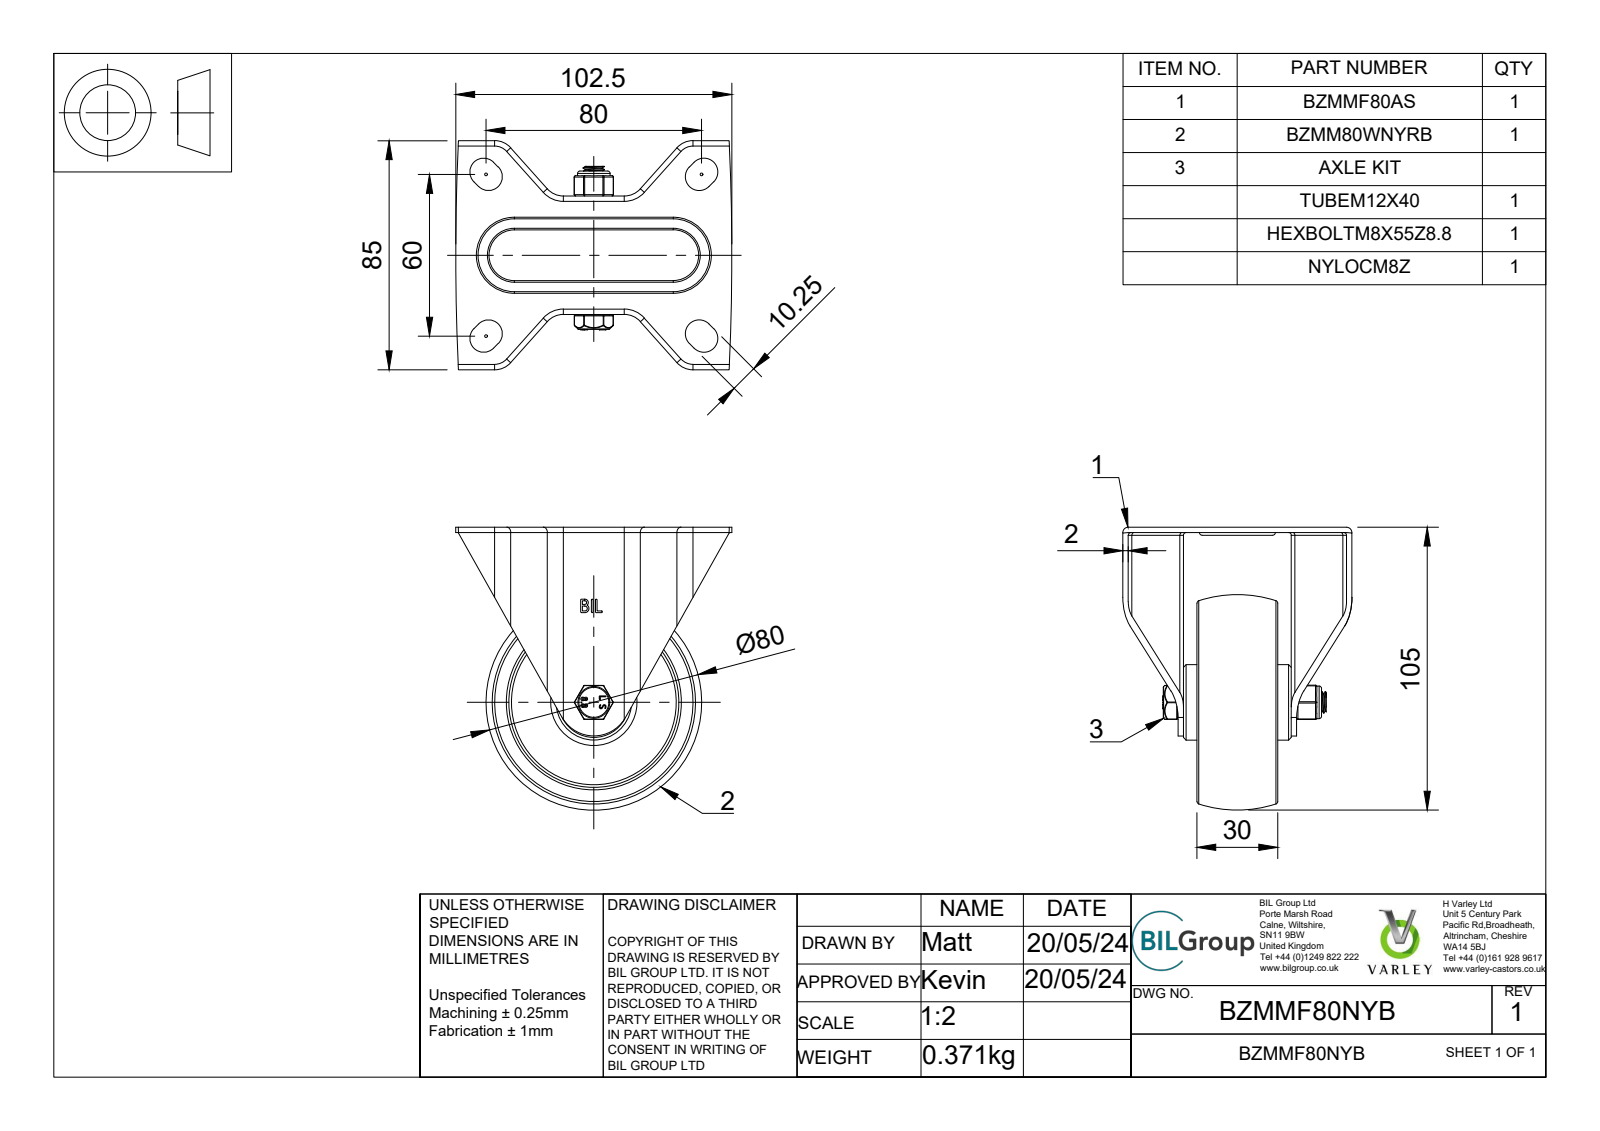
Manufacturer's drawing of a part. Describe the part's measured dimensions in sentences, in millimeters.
The part is named "BZMMF80NYB v4; BZMMF80AS - 40 v2; ZINC PLATED, PRESSED STEEL BRACKET; BZMM80WNYRB v1 (+7 more)". Its 3-D file was written by "Autodesk Translation Framework v13.14.0.145 (AUTOMOTIVE_DESIGN)". It is 16 solids with 501 faces: 195 planar, 206 cylindrical and 100 other. Overall it measures 105 by 102.5 by 85 millimeters. Its volume is 117 157 cubic millimeters and its surface area 73 445 square millimeters. Round holes: 2 of diameter 0.66, 1 of diameter 8, 1 of diameter 8.25, 1 of diameter 8.4, 1 of diameter 8.6, 1 of diameter 12.4, 1 of diameter 12.5, 1 of diameter 23. Round bosses or shafts: 8 of diameter 3.75, 1 of diameter 28, 1 of diameter 19.5, 1 of diameter 12.1, 1 of diameter 11.9, 1 of diameter 11.5, 1 of diameter 7.87, 1 of diameter 6.45. Partial cylindrical surfaces (rounded edges, fillets, slot ends): 18 of radius 0.5, 12 of radius 0.25, 12 of radius 1, 9 of radius 8, 8 of radius 2, 8 of radius 4, 8 of radius 5.12, 4 of radius 0.33. The main face-to-face distances are 2, 18, 22, 5.16, 20, 24, 42, 4, 40, 3.16. The hole center spacings are 3.22, 2.49.
